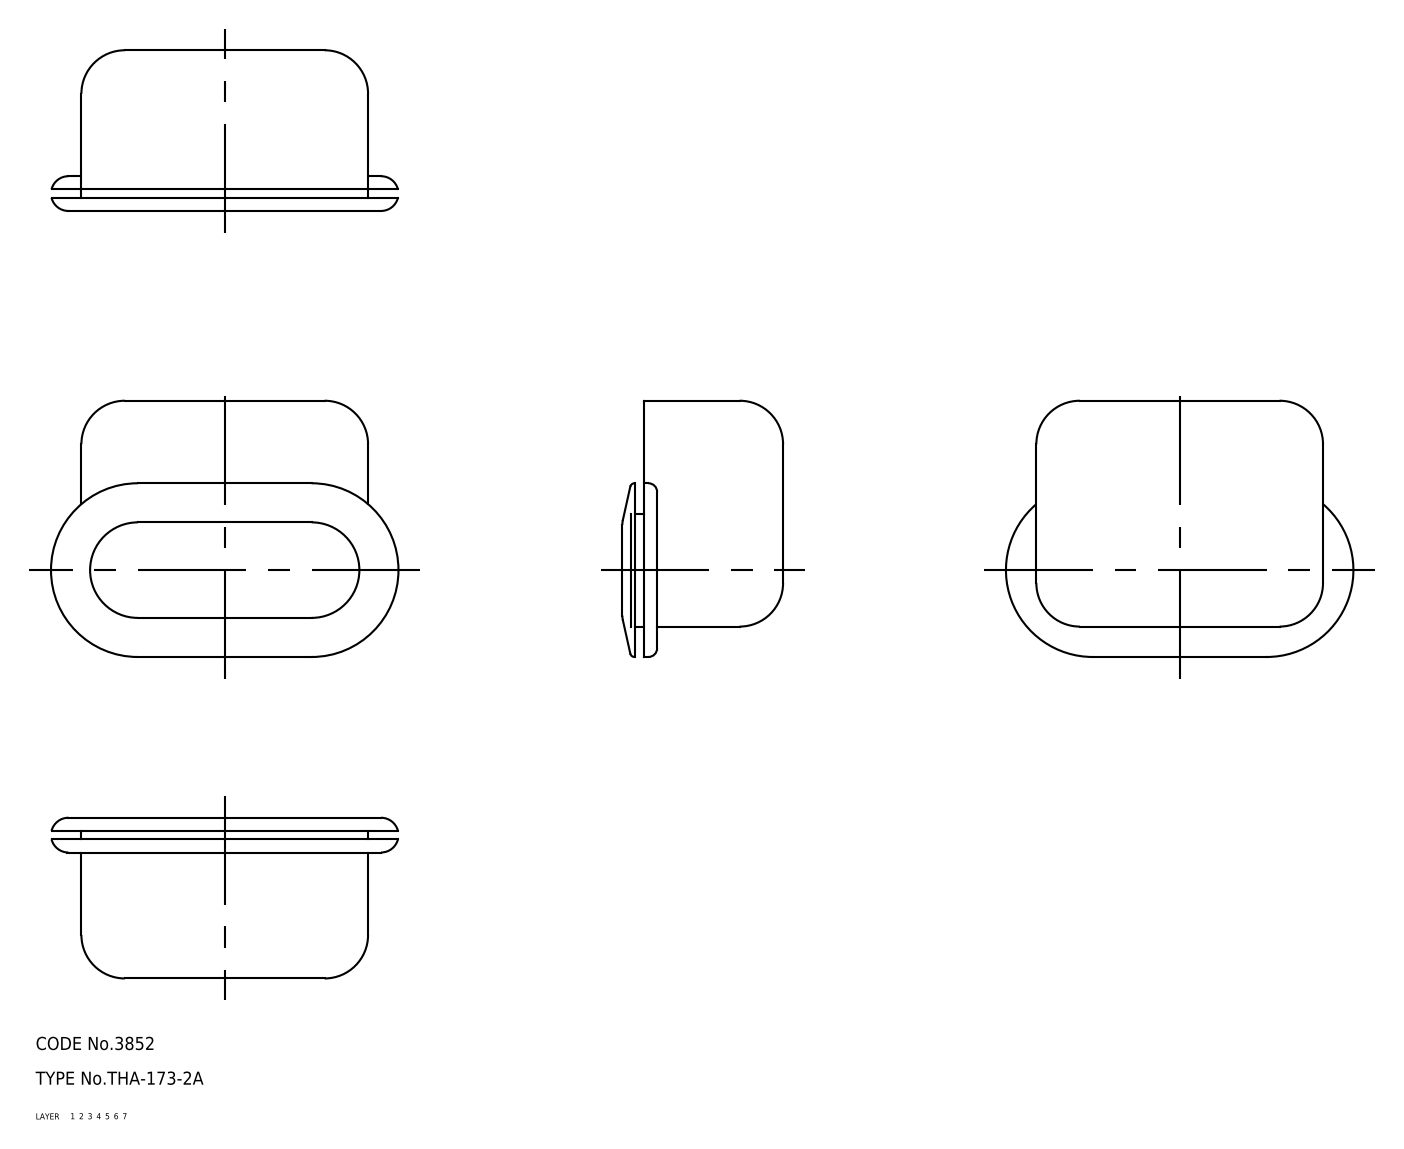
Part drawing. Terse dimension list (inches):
name: pull
written by: CADfix (AUTOMOTIVE_DESIGN)
unit: in
bodies: 1 solid, 82 faces (0 planar, 0 cylindrical, 82 other)
size: 3.15 × 2.323 × 1.457
volume: 1.769 in³; area: 41.46 in²
